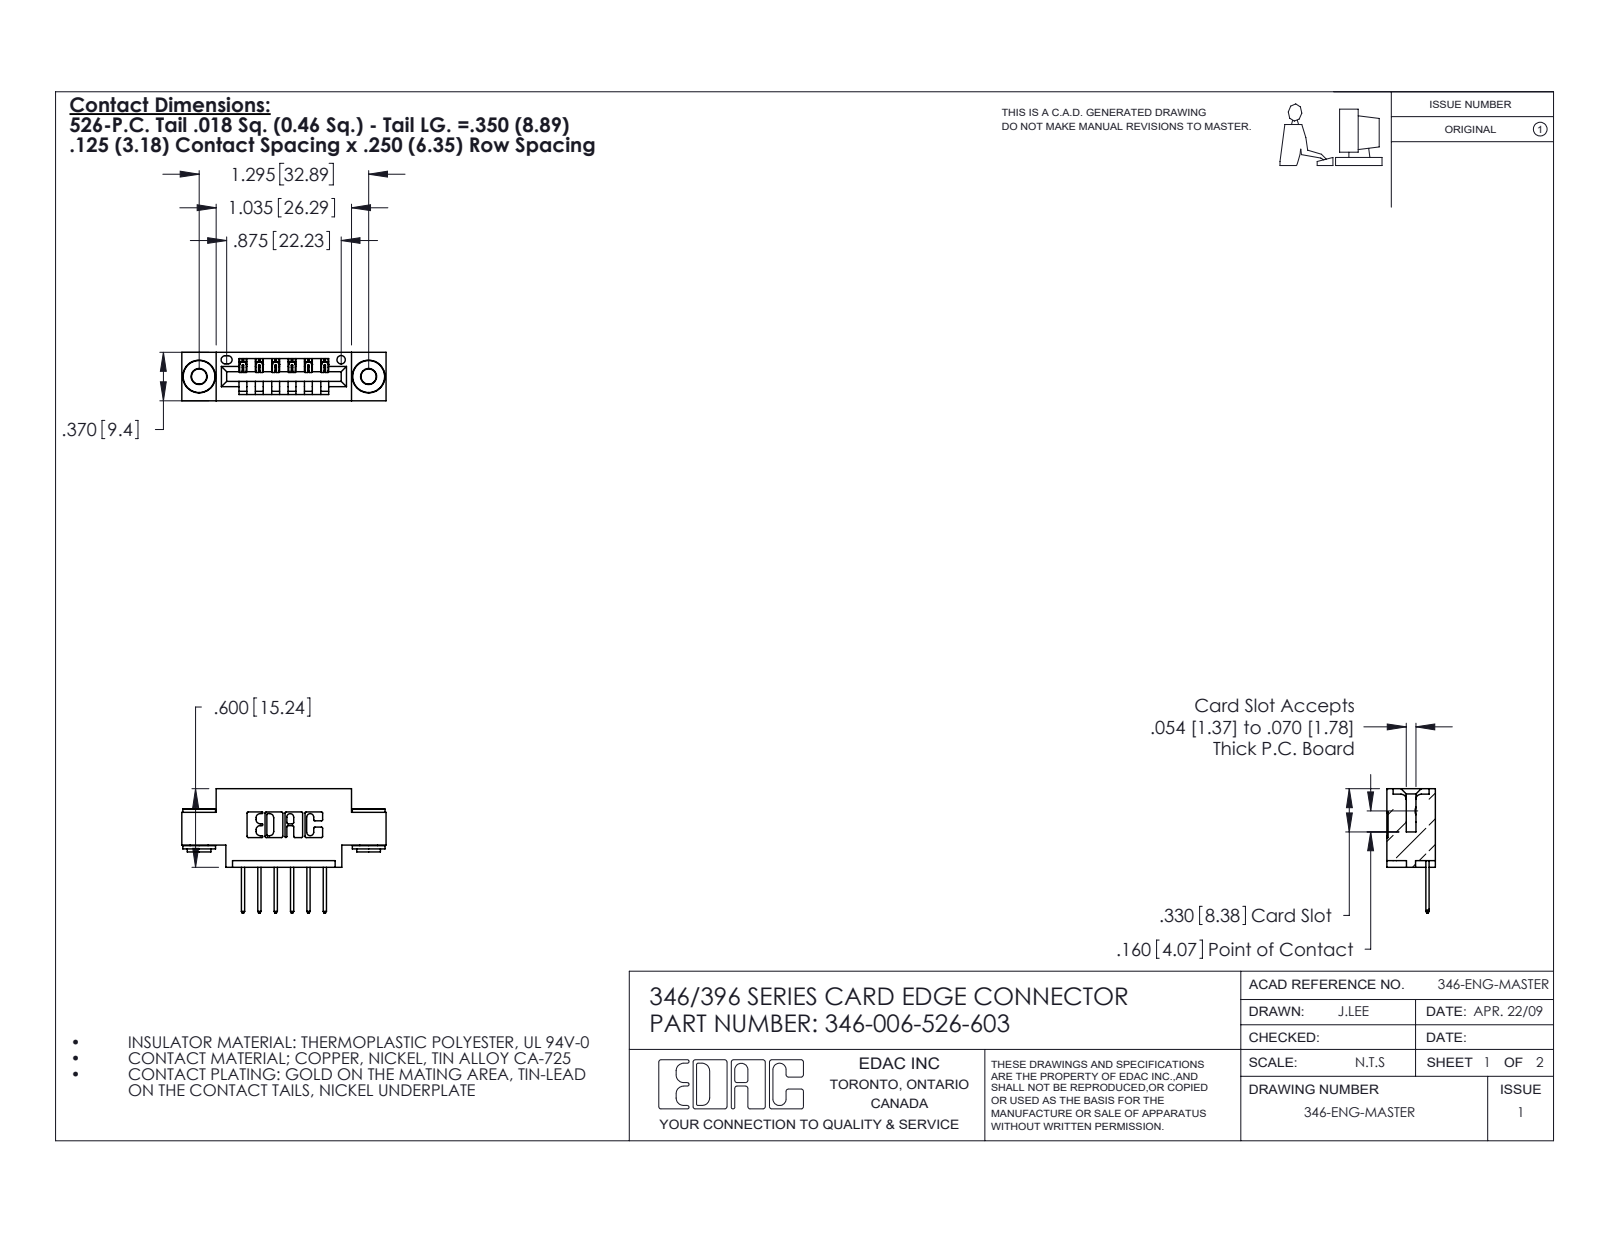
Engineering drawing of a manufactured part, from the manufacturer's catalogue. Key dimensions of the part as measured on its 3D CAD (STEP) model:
Part name (STEP PRODUCT): 346 Part_0.170 Offset - 0.156 Dia-TH; 345-292-001_345-293-126; 346-006-526-603; 345-250-002_345-250-002-102
STEP written by: SolidWorks 2020 (CONFIG_CONTROL_DESIGN)
Units: inches
Bodies: 9 solids, 526 faces (344 planar, 174 cylindrical, 8 other)
Overall size (bounding box): 1.56 × 0.95 × 0.37
Volume: 0.207 in³ · Surface area: 6.588 in²
Round holes (diameter × count): ⌀0.116 ×2, ⌀0.156 ×2, ⌀0.064 ×1
Round bosses / shafts (diameter × count): ⌀0.25 ×2, ⌀0.18 ×2, ⌀0.136 ×2
Partial cylindrical surfaces — rounded edges, fillets, slot ends (radius × count): R0.01 ×22, R0.006 ×12, R0.01 ×12, R0.007 ×6, R0.031 ×6, R0.026 ×3, R0.031 ×2, R0.04 ×2
Main face-to-face distances: 0.25, 0.37, 0.048, 0.322, 0.025, 0.222, 0.148, 0.1, 0.174, 0.072
Hole centre spacings: 0.246, 1.092, 1.295
